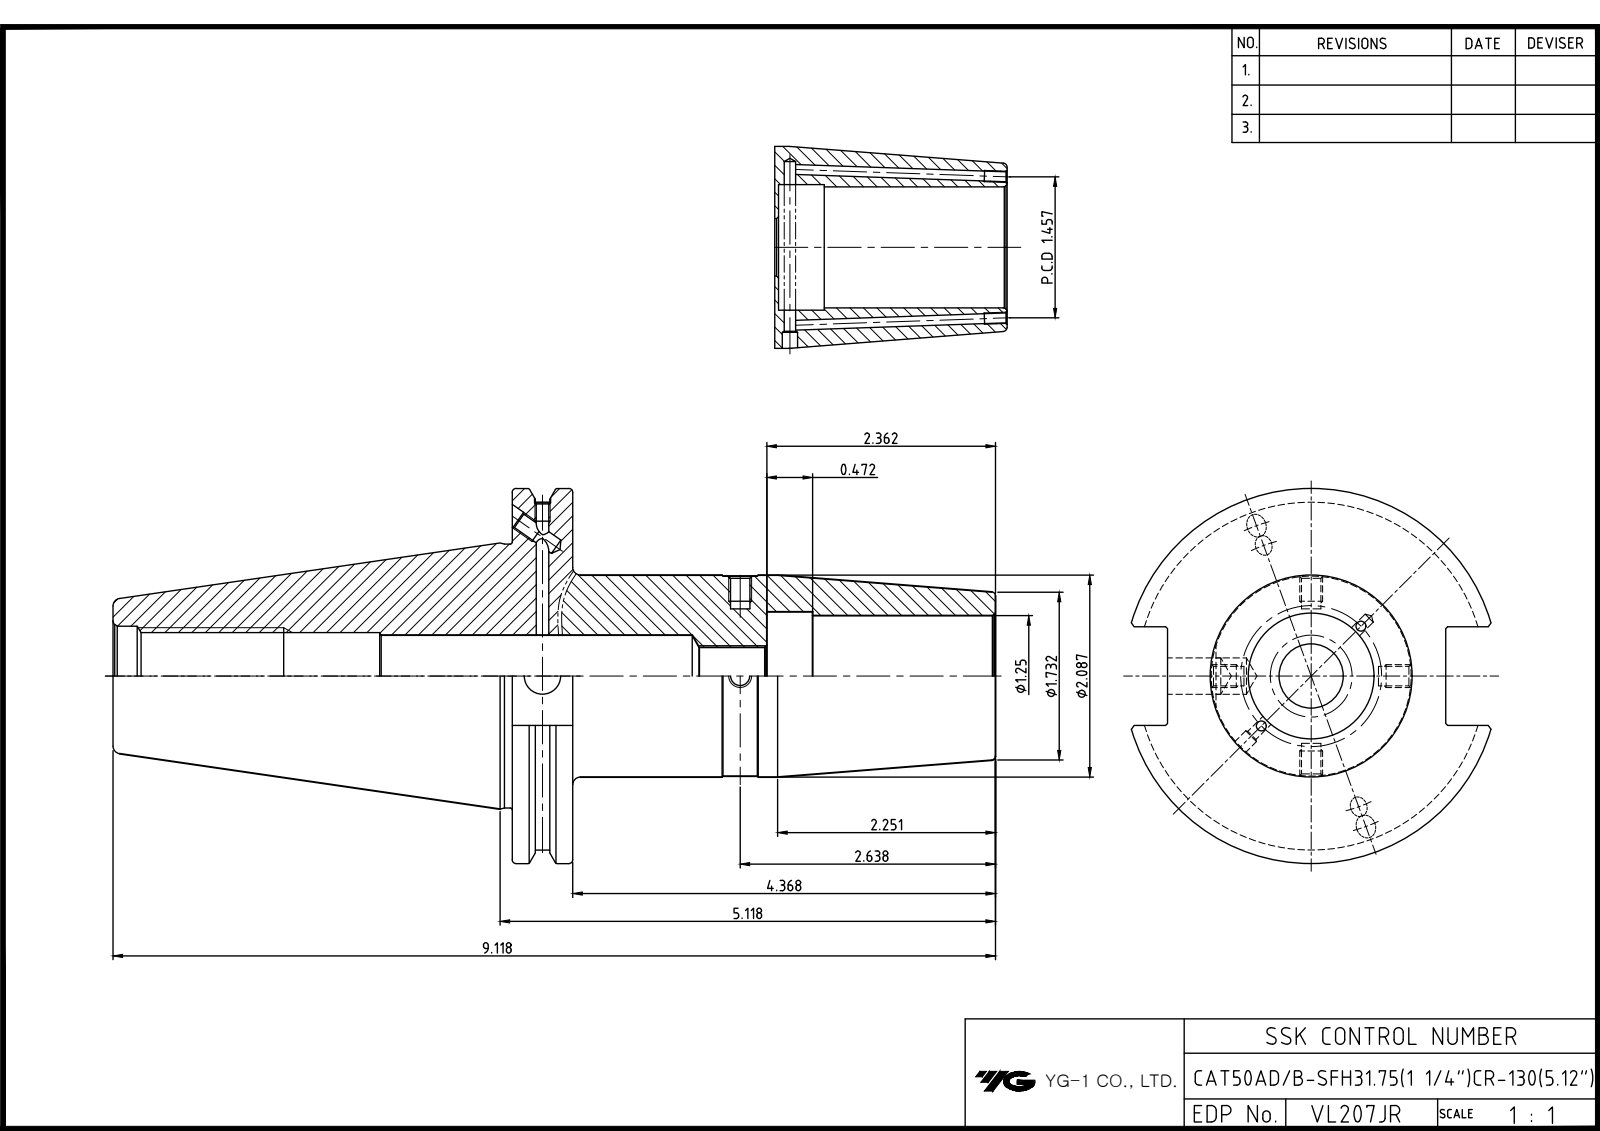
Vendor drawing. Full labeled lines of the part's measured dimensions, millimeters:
Part name (STEP PRODUCT): LO-CAT50ADB-SFH31.75CR-130
STEP written by: Autodesk Inventor 2020 (AUTOMOTIVE_DESIGN)
Units: millimetres
Bodies: 1 solid, 93 faces (38 planar, 29 cylindrical, 26 other)
Overall size (bounding box): 231.6 × 98.42 × 94.69
Volume: 478 502 mm³ · Surface area: 72 220 mm²
Round holes (diameter × count): ⌀2.46 ×2, ⌀3.24 ×2, ⌀4.13 ×2, ⌀4.2 ×2, ⌀5 ×2, ⌀9.53 ×1, ⌀14.92 ×1, ⌀21.5 ×1, ⌀21.97 ×1, ⌀26.2 ×1, ⌀31.75 ×1, ⌀33 ×1
Round bosses / shafts (diameter × count): ⌀98.42 ×1, ⌀91.29 ×1, ⌀69.25 ×1, ⌀53 ×1
Main face-to-face distances: 15.88, 66.83, 50.95, 104.77, 120.65, 171.6, 231.4, 126.63, 110.75, 59.8
